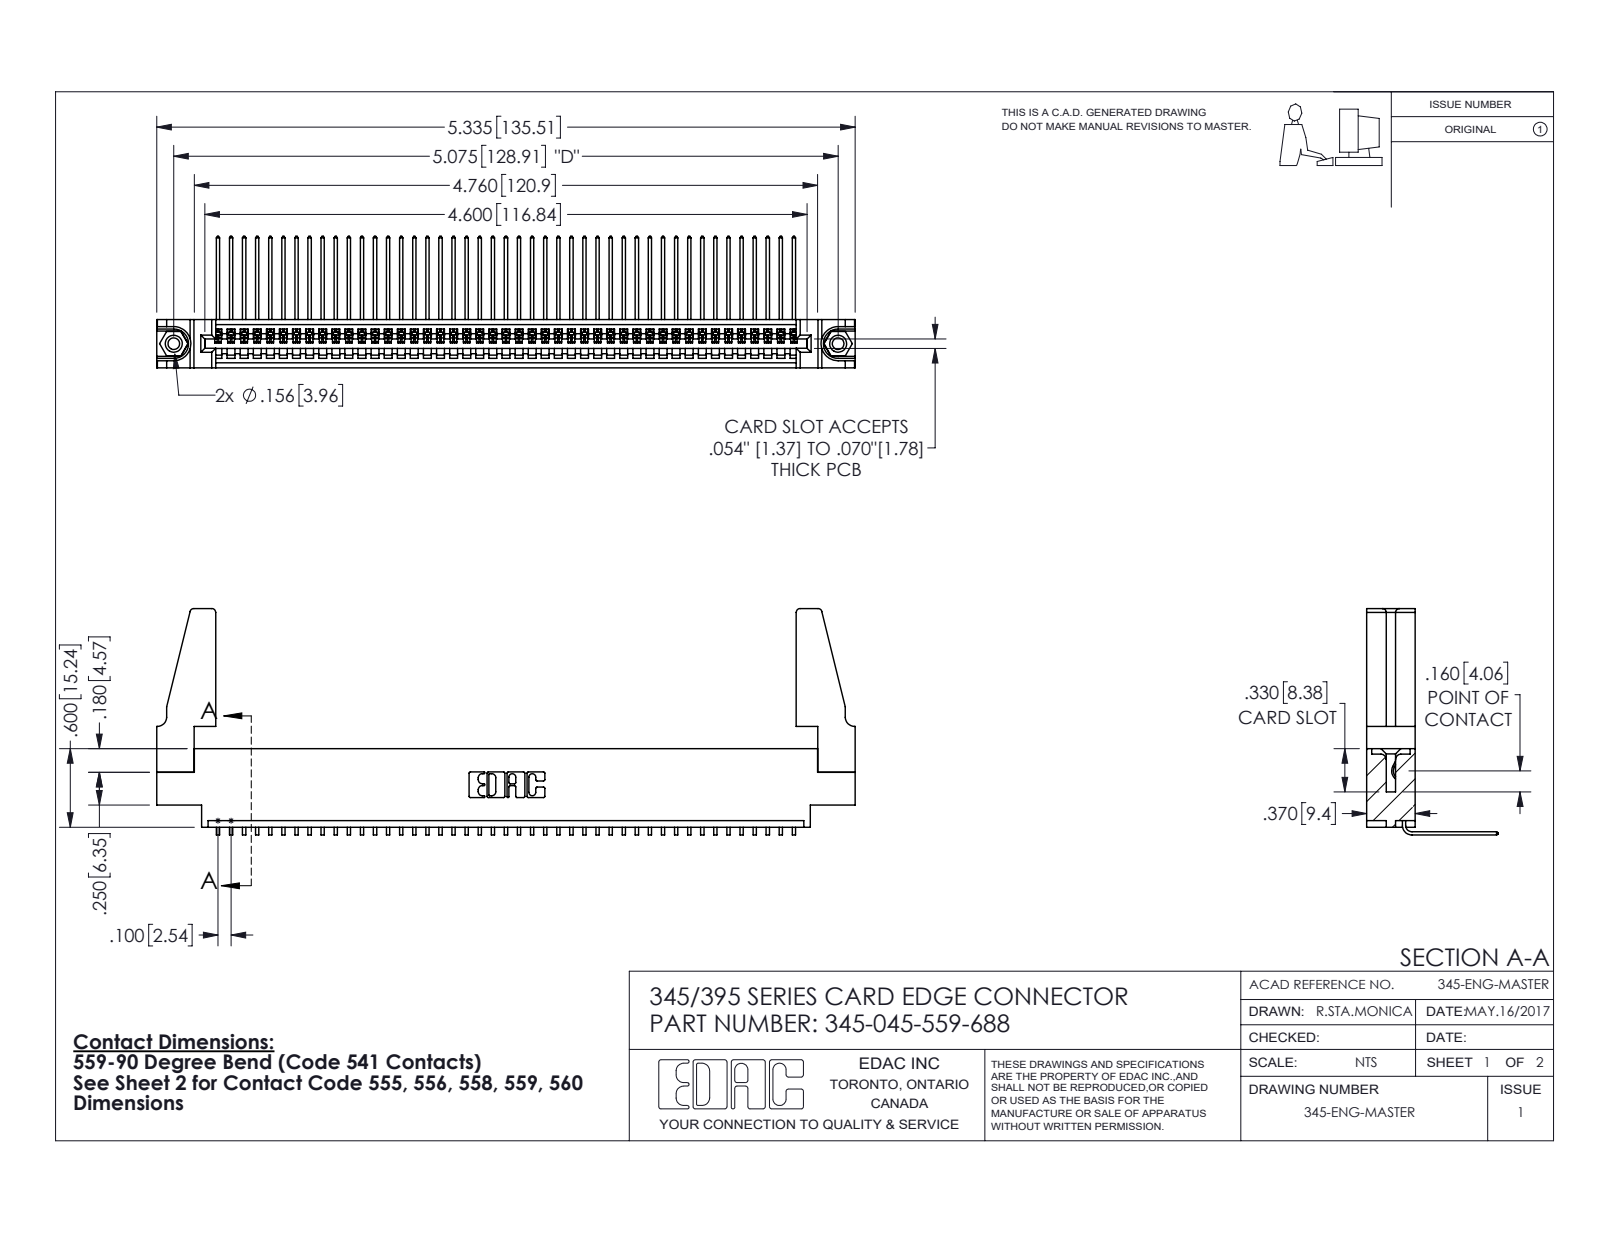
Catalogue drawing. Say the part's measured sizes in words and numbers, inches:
The part is named "345-250-001_345-250-001-102; 345-045-559-688; 345 Part_0.170 Offset - 0.156 Dia-TH; 345-220-078_345-220-088 (+1 more)". Its 3-D file was written by "SolidWorks 2016 (CONFIG_CONTROL_DESIGN)". It is 50 solids with 2954 faces: 2046 planar, 892 cylindrical and 16 other. Overall it measures 5.336 by 1.729 by 1.005 inches. Its volume is 0.988 cubic inches and its surface area 33.12 square inches. Round holes: 2 of diameter 0.089, 2 of diameter 0.125, 2 of diameter 0.156, 1 of diameter 0.064. Round bosses or shafts: 2 of diameter 0.155. Partial cylindrical surfaces (rounded edges, fillets, slot ends): 90 of radius 0.006, 22 of radius 0.01, 8 of radius 0.03, 6 of radius 0.007, 6 of radius 0.031, 3 of radius 0.026, 2 of radius 0.031, 2 of radius 0.04. The main face-to-face distances are 0.072, 0.37, 0.298, 0.2, 0.098, 0.272, 0.025, 0.225, 0.175, 0.149. The hole center spacings are 0.27, 4.839, 5.075.
